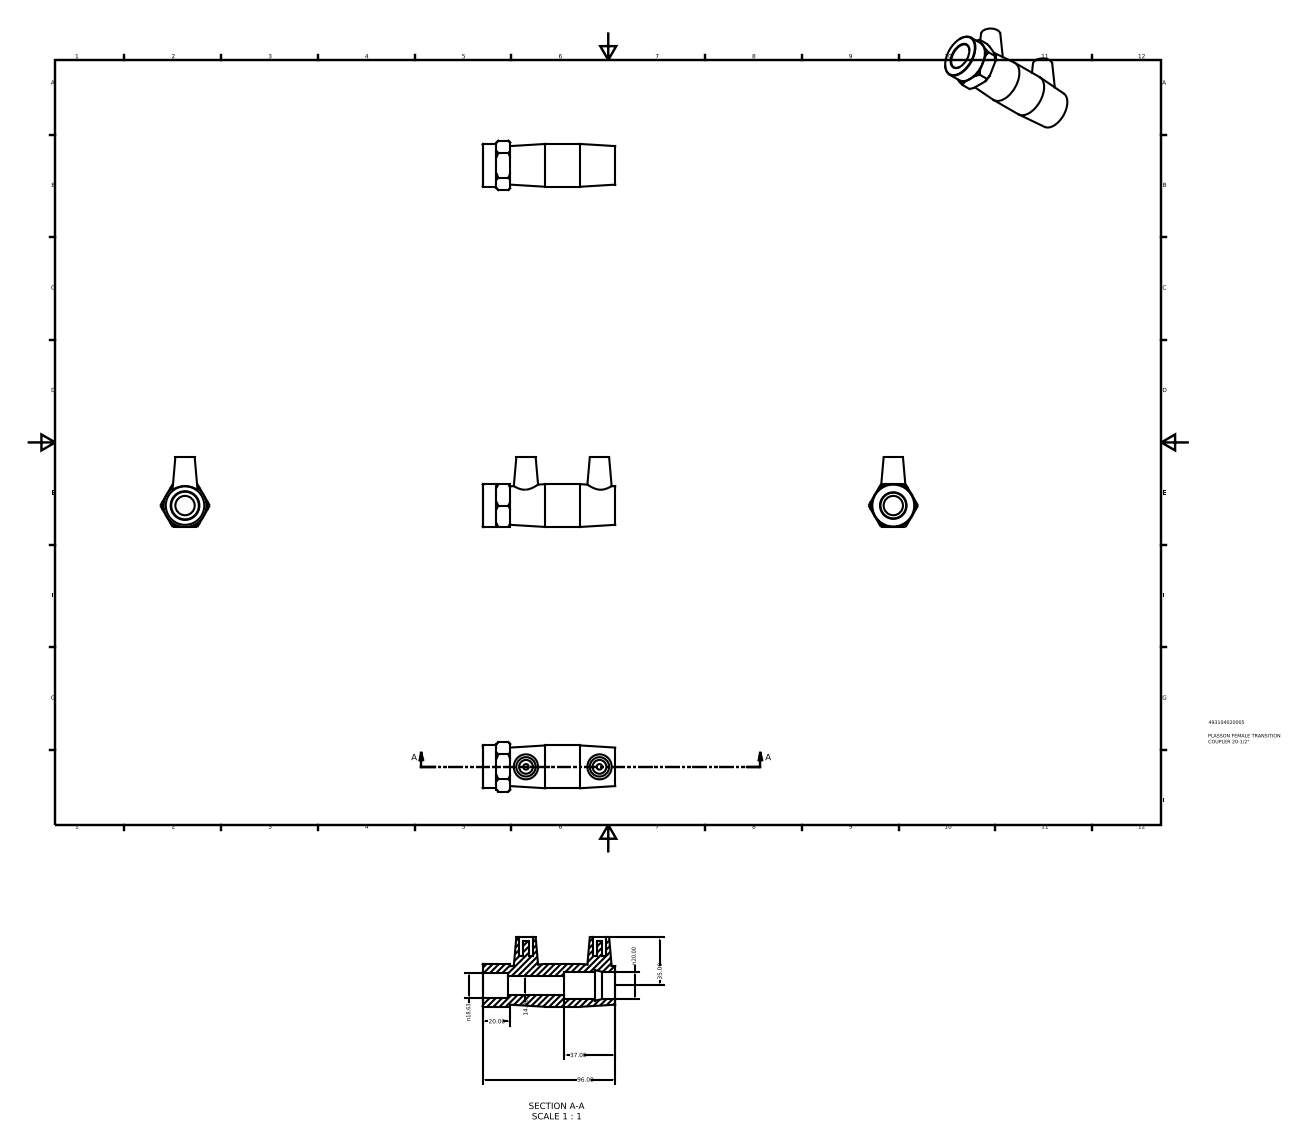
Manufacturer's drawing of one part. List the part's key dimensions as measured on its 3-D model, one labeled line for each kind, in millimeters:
Part name (STEP PRODUCT): 493104020005
STEP written by: Autodesk Inventor 2015 (AUTOMOTIVE_DESIGN)
Units: millimetres
Bodies: 1 solid, 54 faces (24 planar, 10 cylindrical, 20 other)
Overall size (bounding box): 96 × 50.5 × 35.8
Volume: 52 917 mm³ · Surface area: 18 897 mm²
Round holes (diameter × count): ⌀10 ×2, ⌀14 ×1, ⌀18.63 ×1, ⌀20 ×1
Round bosses / shafts (diameter × count): ⌀4 ×2, ⌀31 ×1
Main face-to-face distances: 31, 96, 20, 76, 59, 39, 37, 50.5, 19.5, 36.5
Hole centre spacings: 53.2
